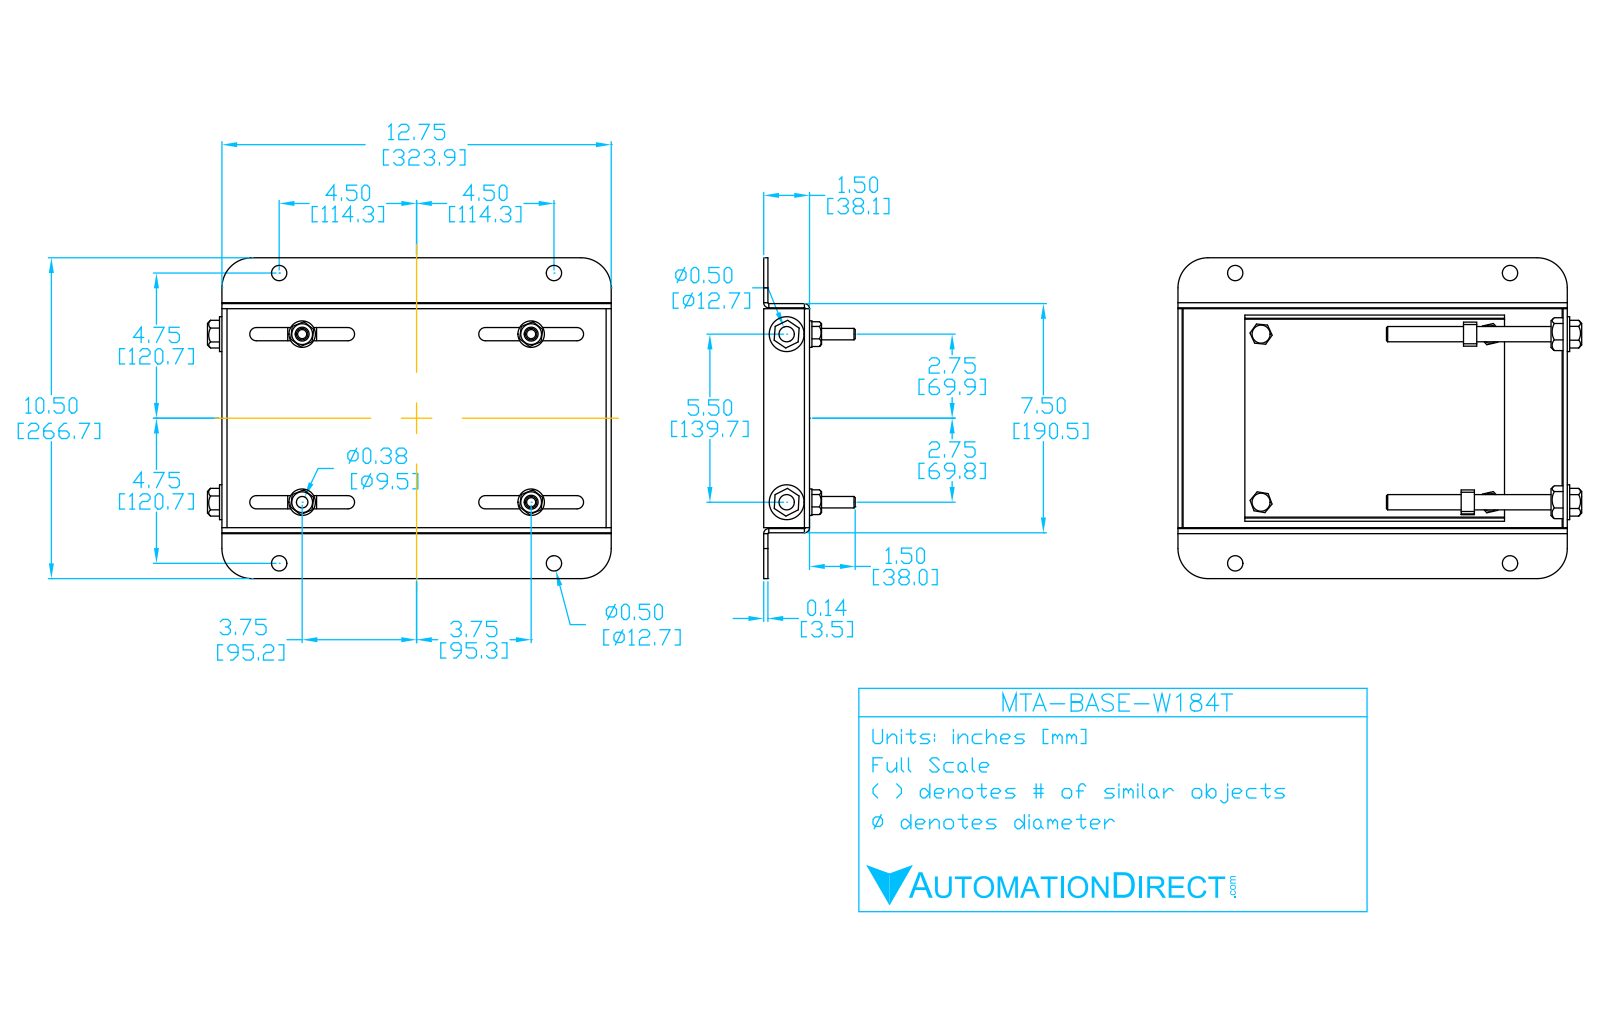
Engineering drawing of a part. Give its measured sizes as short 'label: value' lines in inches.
name: W184T
written by: SolidWorks 2017 (AUTOMOTIVE_DESIGN)
unit: in
bodies: 20 solids, 322 faces (158 planar, 108 cylindrical, 56 other)
size: 13.262 × 10.5 × 3.006
volume: 36.53 in³; area: 563.1 in²
holes: 6× ⌀0.5, 4× ⌀0.375, 4× ⌀0.378, 2× ⌀0.531, 2× ⌀0.63
bosses: 4× ⌀0.866, 2× ⌀1.142
rounds: 8× R0.029, 8× R0.079, 8× R0.217, 6× R0.167, 4× R0.984, 2× R0.135
face distances: 0.138, 1.362, 0.106, 0.244, 1.5, 1.256, 1.224, 1.118, 7.362, 12.613
hole spacings: 7.5, 0.028, 5.472, 5.5, 2.135, 3.007, 7.044, 7.537
